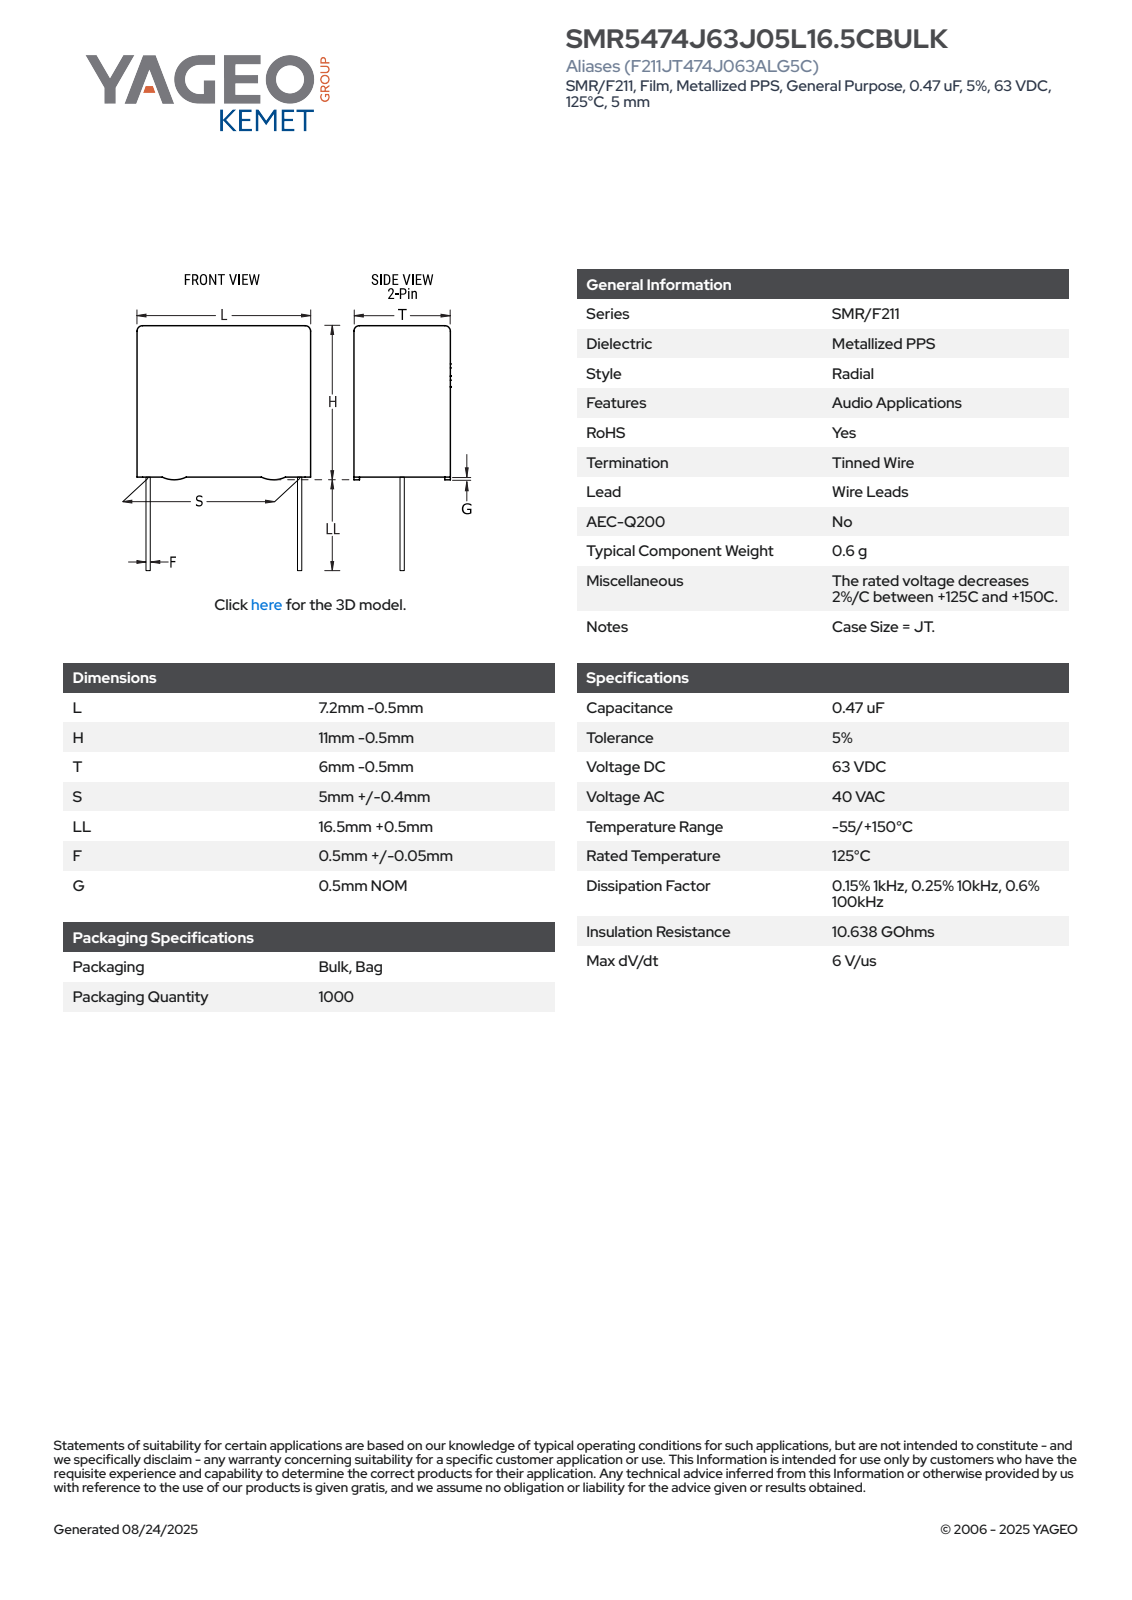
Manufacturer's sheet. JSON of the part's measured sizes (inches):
{"part_name": "CFR_RBG_7.2X11X6_L6.7H10.5T5.5S5LL17F0.55G0.5", "step_written_by": "SolidWorks 2021 (AUTOMOTIVE_DESIGN)", "units": "inches", "bodies": {"solids": 4, "faces": 89, "planar": 81, "cylindrical": 8, "other": 0}, "overall_size": [1.083, 0.264, 0.217], "volume_in3": 0.023, "surface_area_in2": 0.594, "round_bosses_or_shafts": [[0.022, 2]], "partial_cylinders_radius": [[0.02, 4]], "face_to_face_distances": [0.217, 0.264, 0.394, 0.204, 0.012, 0.02, 0.413, 0.192, 0.098, 0.669]}
